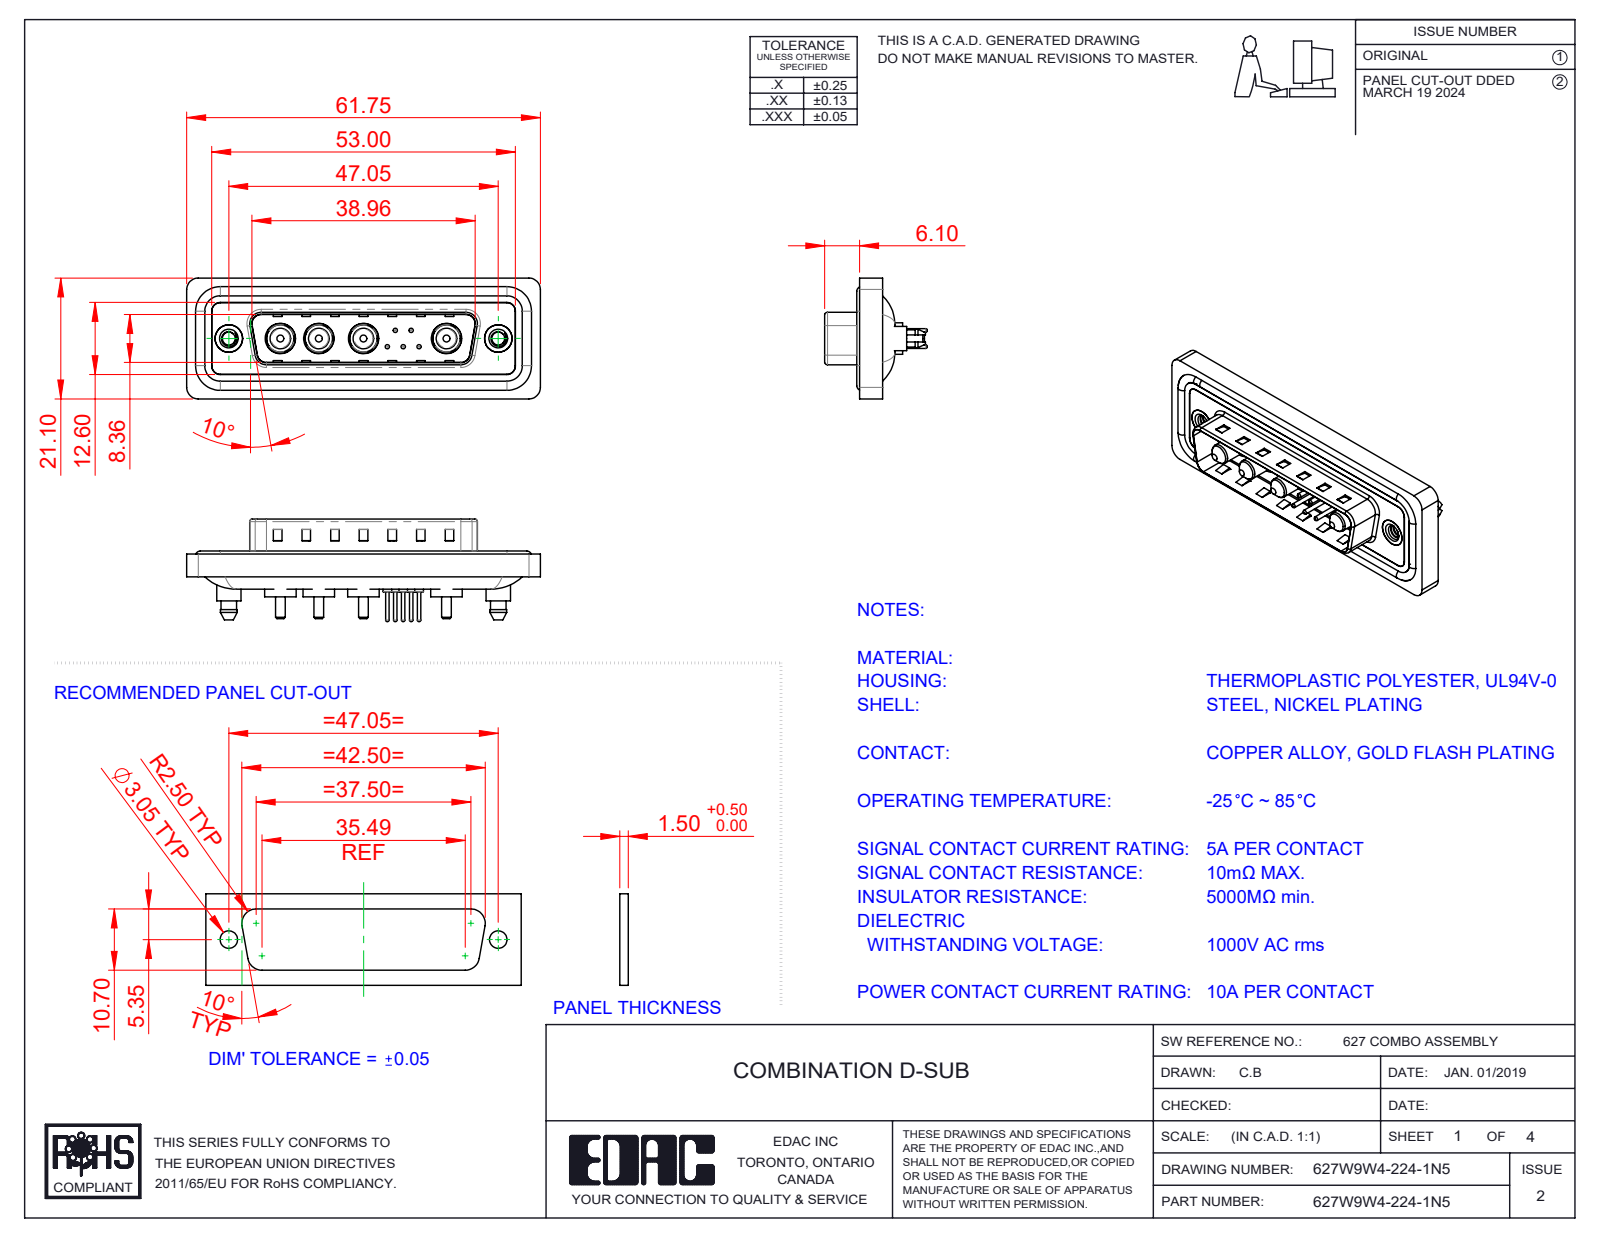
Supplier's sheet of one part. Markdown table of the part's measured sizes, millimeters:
| quantity | value |
| --- | --- |
| part name | 627Combo Housing_9W4; 627Combo Waterproof Housing_25 Contacts; 627Combo Shell Front_25 Contacts; 627Combo Contact Row 1_24 (+5 more) |
| STEP written by | SolidWorks 2023 (CONFIG_CONTROL_DESIGN) |
| units | millimeters |
| bodies | 20 solids, 874 faces (300 planar, 366 cylindrical, 208 other) |
| overall size | 61.75 × 21.1 × 17.9 |
| volume | 7 479 mm³ |
| surface area | 12 118 mm² |
| round holes (diameter × count) | 0.75 × 5, 1.6 × 5, 2 × 5, 4.85 × 4, 5.3 × 4, 2.26 × 2, 4 × 2, 4.8 × 2, 5 × 2 |
| round bosses / shafts (diameter × count) | 1.5 × 5, 0.6 × 5, 5.5 × 4, 5.2 × 4, 4.75 × 4, 3.75 × 4, 3.6 × 4, 1.7 × 4 |
| partial cylindrical surfaces (radius × count) | 1.5 × 24, 2 × 18, 1.6 × 10, 0.5 × 8, 0.25 × 4, 0.6 × 4, 0.65 × 4, 0.9 × 4 |
| main face-to-face distances | 0.4, 1.5, 1.1, 0.5, 1.6, 3.1, 2.9, 0.82, 9.58, 5.65 |
| hole center spacings | 3.16, 2.77, 5.04, 14.51, 2.78, 4.4, 4.41, 5 |
